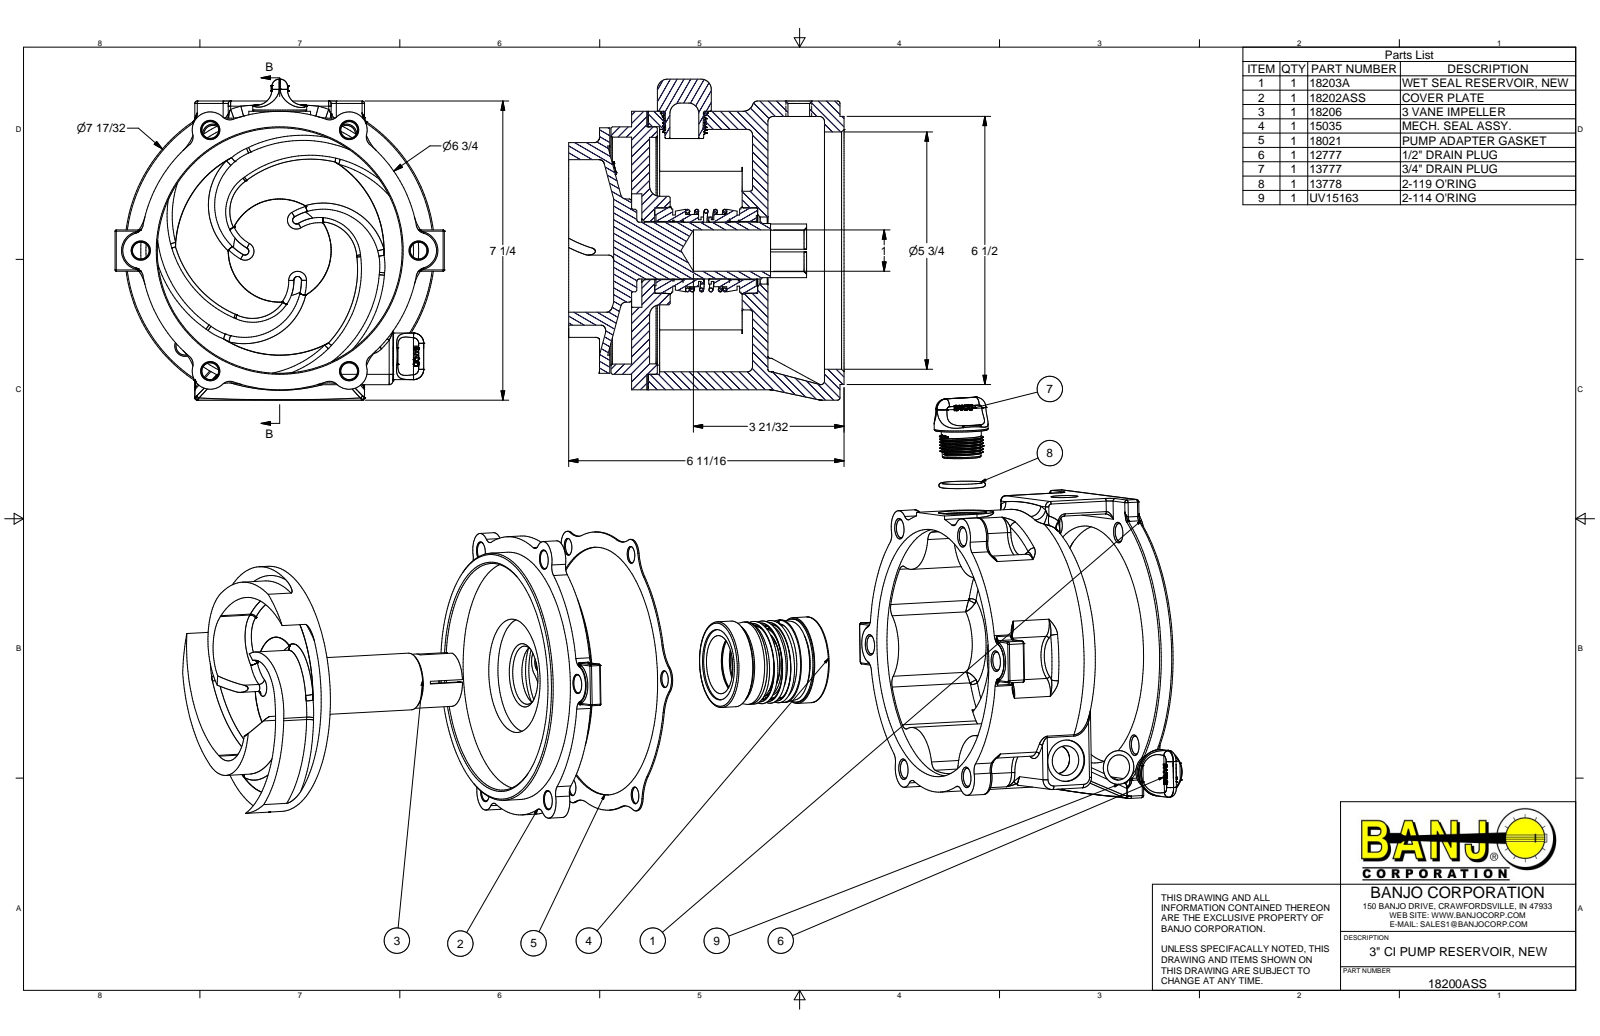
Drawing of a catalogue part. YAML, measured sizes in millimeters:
part_name: "18200ASS; 18203A; 18202ASS; 18206 (+6 more)"
step_written_by: "Autodesk Inventor 2013 (AUTOMOTIVE_DESIGN)"
units: millimeters
bodies: {solids: 11, faces: 1460, planar: 412, cylindrical: 331, other: 717}
overall_size: [203.2, 197.6, 170]
volume: 1508000
surface_area: 383100
round_holes:
  - {diameter: 11.1, count: 10}
  - {diameter: 10.3, count: 6}
  - {diameter: 12.7, count: 1}
  - {diameter: 13.4, count: 1}
  - {diameter: 17.5, count: 1}
  - {diameter: 17.8, count: 1}
  - {diameter: 25.4, count: 1}
  - {diameter: 25.5, count: 1}
  - {diameter: 25.9, count: 1}
  - {diameter: 29.7, count: 1}
  - {diameter: 34.9, count: 1}
  - {diameter: 35.8, count: 1}
round_bosses_or_shafts:
  - {diameter: 171.5, count: 1}
  - {diameter: 152.3, count: 1}
  - {diameter: 152.3, count: 1}
  - {diameter: 151.1, count: 1}
  - {diameter: 66.8, count: 1}
  - {diameter: 63.5, count: 1}
  - {diameter: 52.8, count: 1}
  - {diameter: 51.2, count: 1}
partial_cylinders:
  - {radius: 1.5, count: 31}
  - {radius: 0.8, count: 28}
  - {radius: 6.4, count: 28}
  - {radius: 25.4, count: 21}
  - {radius: 9.5, count: 20}
  - {radius: 3.2, count: 16}
  - {radius: 11.1, count: 9}
  - {radius: 15.1, count: 6}
face_to_face_distances: [9.5, 84.1, 74.6, 119, 6.4, 10.3, 0.8, 73.8, 73, 68.2]
hole_center_spacings: [85.7, 85.7, 148.5, 84.2, 171.5, 3.2, 21.9, 64.8]
